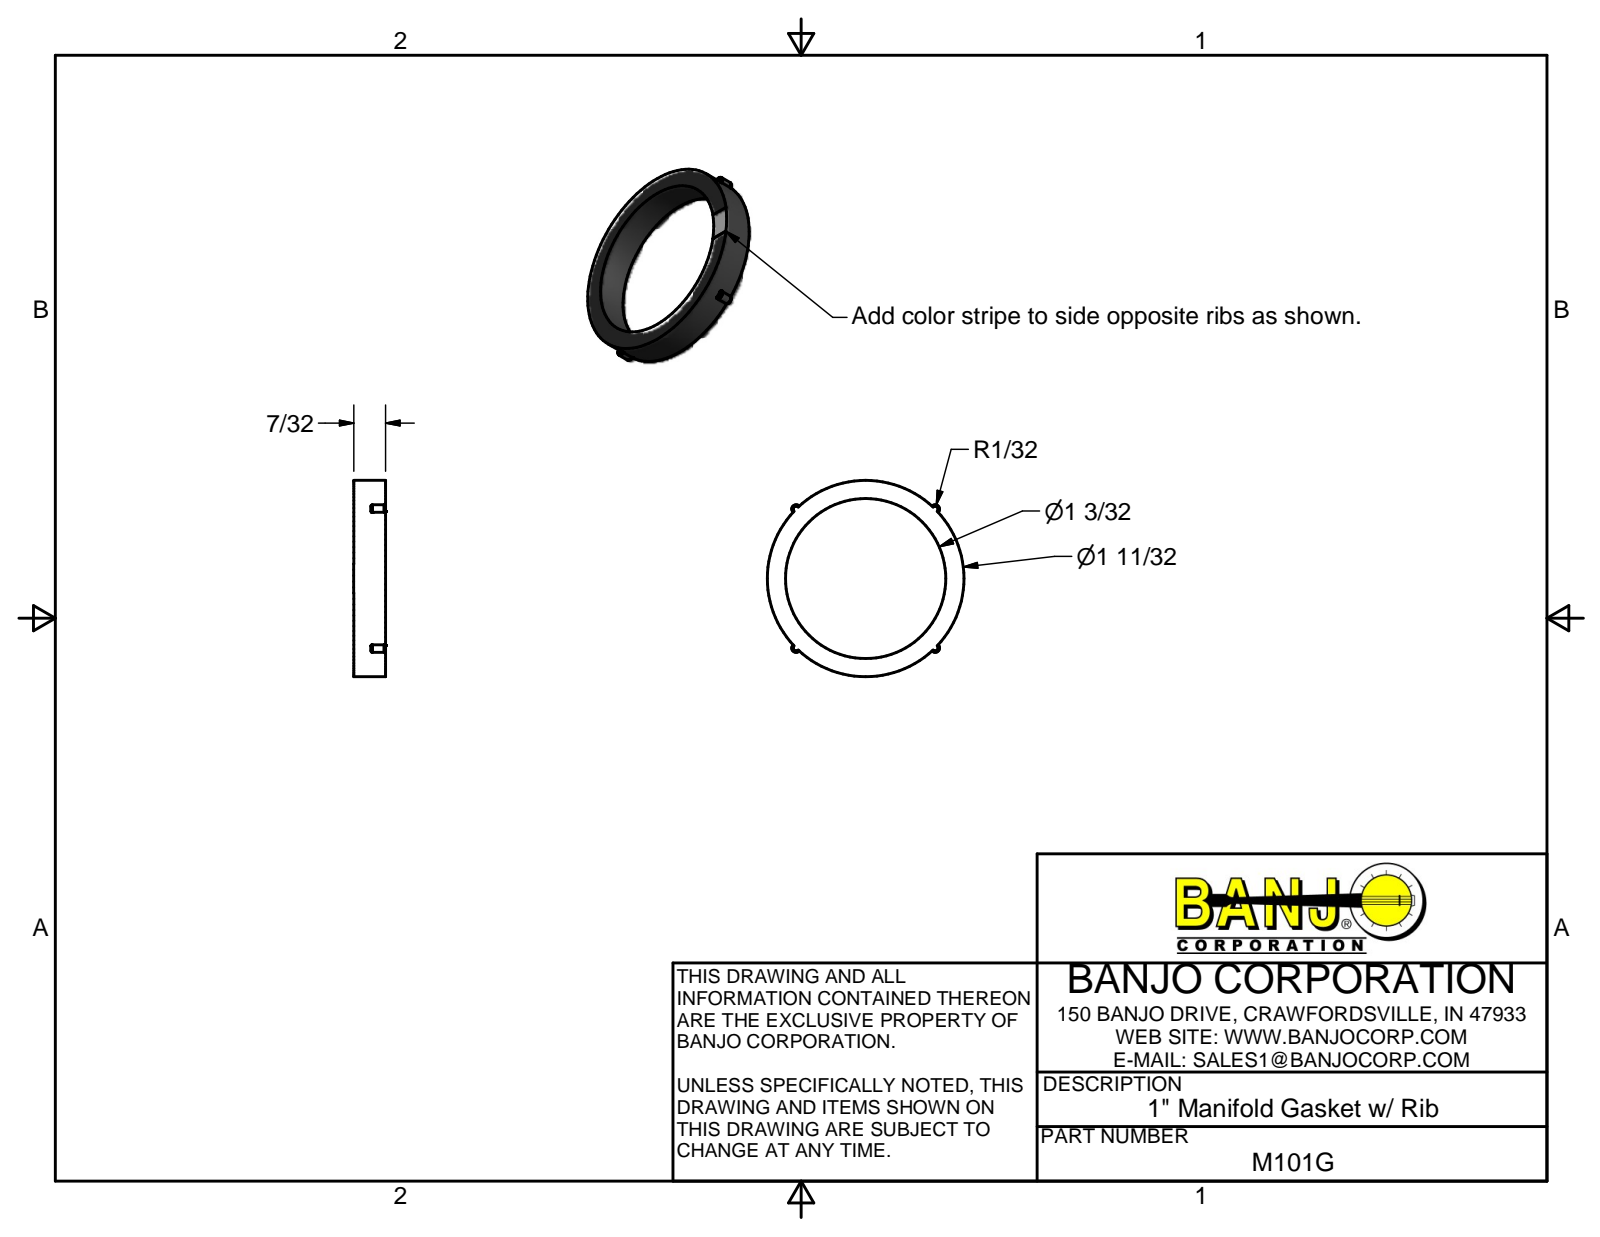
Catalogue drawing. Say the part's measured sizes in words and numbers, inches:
The part is named "M101G". Its 3-D file was written by "Autodesk Inventor 2011 (AUTOMOTIVE_DESIGN)". It is 1 solid with 23 faces: 9 planar, 6 cylindrical and 8 other. Overall it measures 1.35 by 1.35 by 0.219 inches. Its volume is 0.105 cubic inches and its surface area 2.663 square inches. Round holes: 1 of diameter 1.1. Round bosses or shafts: 1 of diameter 1.35. Partial cylindrical surfaces (rounded edges, fillets, slot ends): 4 of radius 0.03. The main face-to-face distances are 0.218, 0.219, 0.119, 0.118, 0.1, 0.2.
